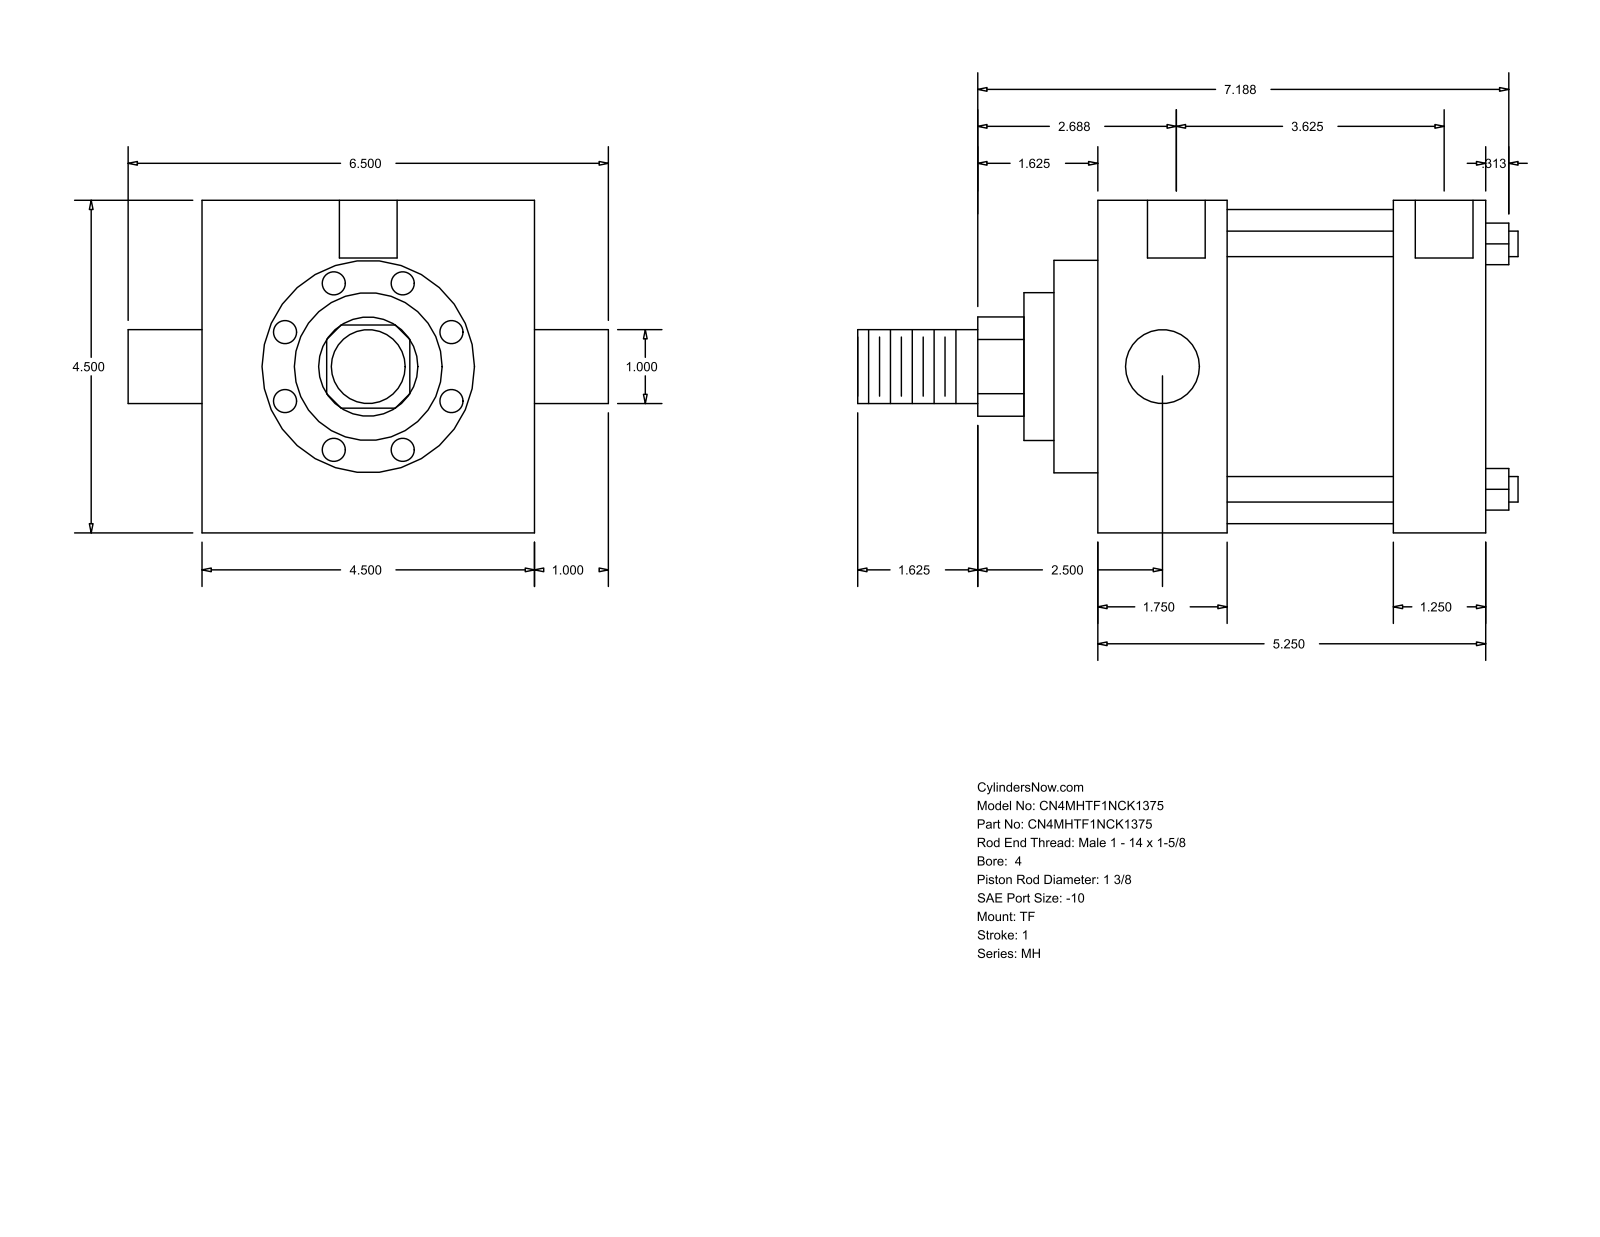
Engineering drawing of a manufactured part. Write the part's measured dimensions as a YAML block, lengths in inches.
part_name: "MH_TF__0400_1.375"
step_written_by: "GSSL Pune (CONFIG_CONTROL_DESIGN)"
units: inches
bodies: {solids: 0, faces: 86, planar: 61, cylindrical: 25, other: 0}
overall_size: [8.937, 6.5, 4.5]
round_holes:
  - {diameter: 0.344, count: 3}
  - {diameter: 0.781, count: 2}
round_bosses_or_shafts:
  - {diameter: 0.345, count: 4}
  - {diameter: 1, count: 2}
  - {diameter: 4.25, count: 1}
  - {diameter: 2.875, count: 1}
  - {diameter: 2, count: 1}
  - {diameter: 1.375, count: 1}
partial_cylinders:
  - {radius: 0.672, count: 1}
face_to_face_distances: [4.5, 5.25, 1.75, 3.5, 4, 2.25, 1.25, 0.594, 2.344, 4.594]
hole_center_spacings: [0.063, 3.688, 3.625, 3.75]
